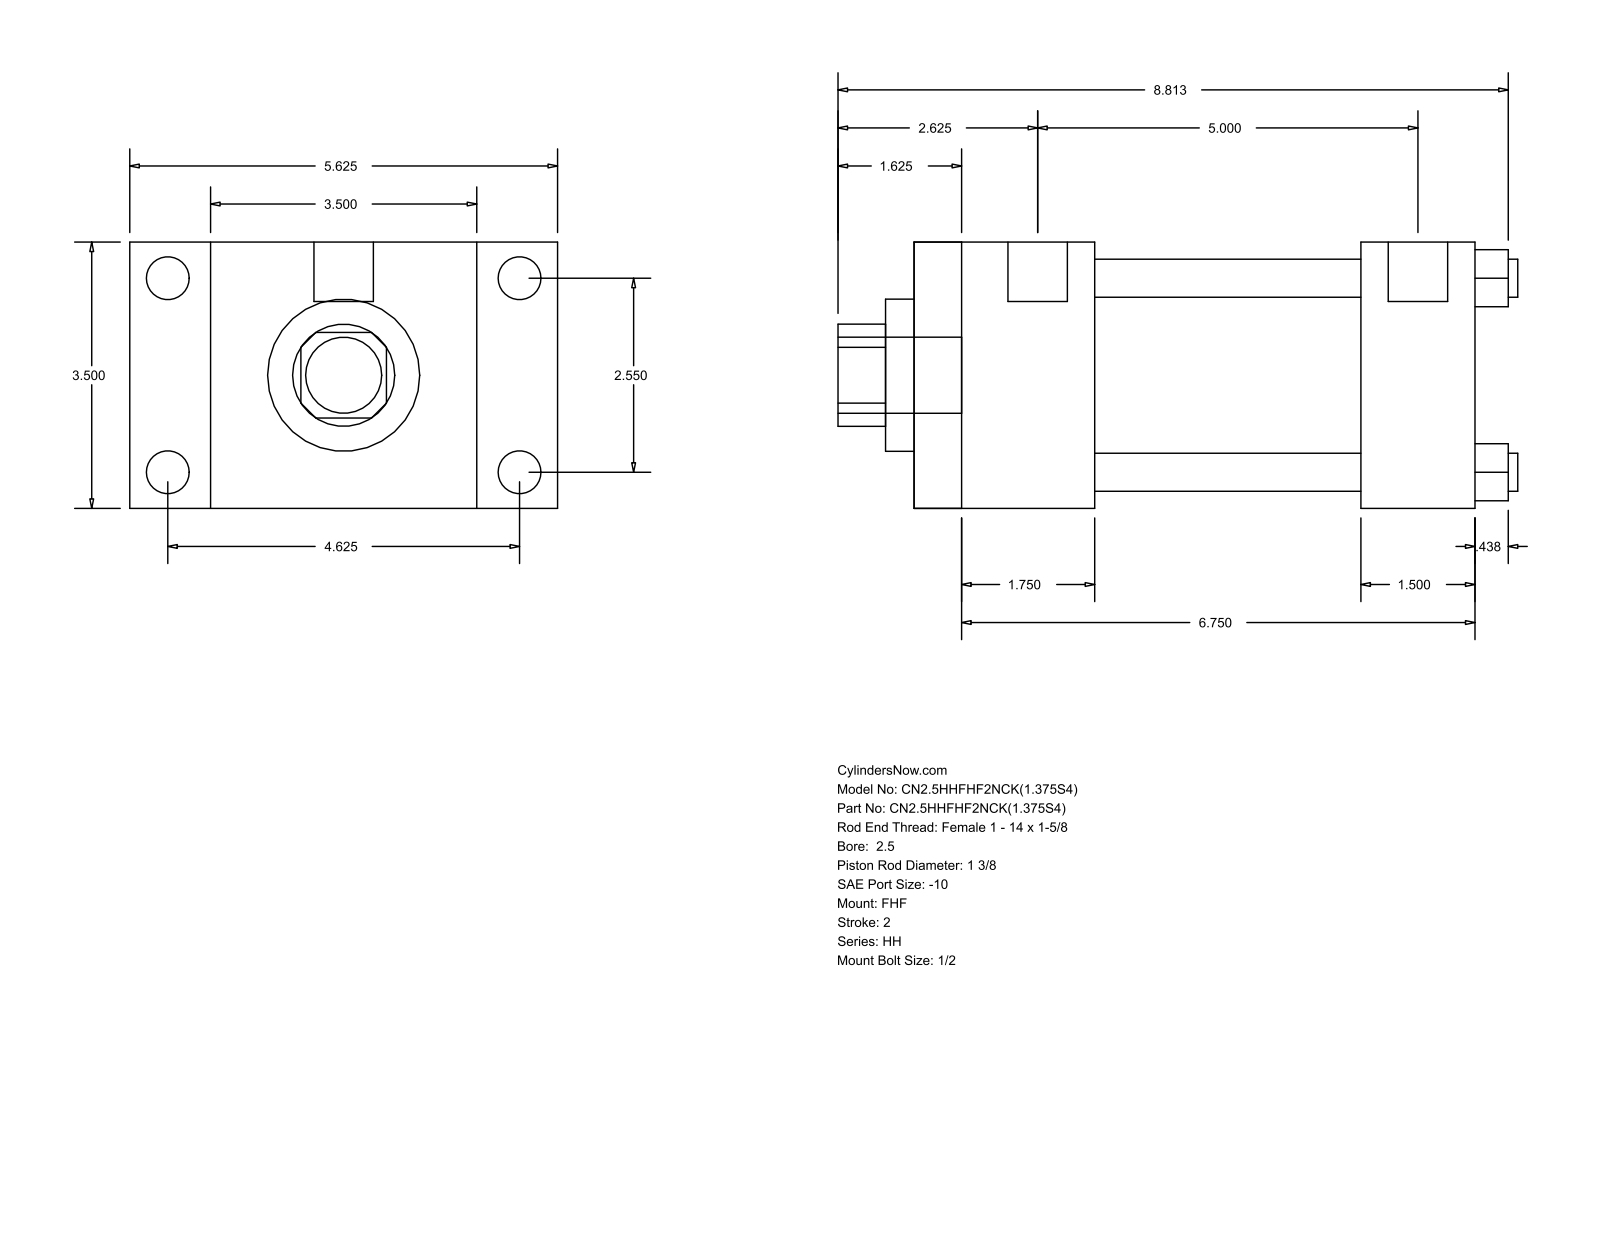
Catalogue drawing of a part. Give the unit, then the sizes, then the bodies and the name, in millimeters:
Units: millimetres
Overall size (bounding box): 227.01 × 142.88 × 88.9
Round holes (diameter × count): ⌀12.7 ×4, ⌀34.92 ×1, ⌀50.8 ×1, ⌀73.03 ×1
Round bosses / shafts (diameter × count): ⌀14.3 ×4, ⌀5.56 ×4, ⌀19.84 ×2, ⌀25.4 ×1
Partial cylindrical surfaces — rounded edges, fillets, slot ends (radius × count): R17.06 ×1
Main face-to-face distances: 88.9, 60.32, 26.99, 115.89, 187.32, 127, 142.88, 149.22, 38.1, 19.05
Hole centre spacings: 45.79, 64.76, 91.58
Bodies: 0 solids, 88 faces (60 planar, 28 cylindrical, 0 other)
Part name (STEP PRODUCT): HH_FHF__0250_1.375
STEP written by: GSSL Pune (CONFIG_CONTROL_DESIGN)
